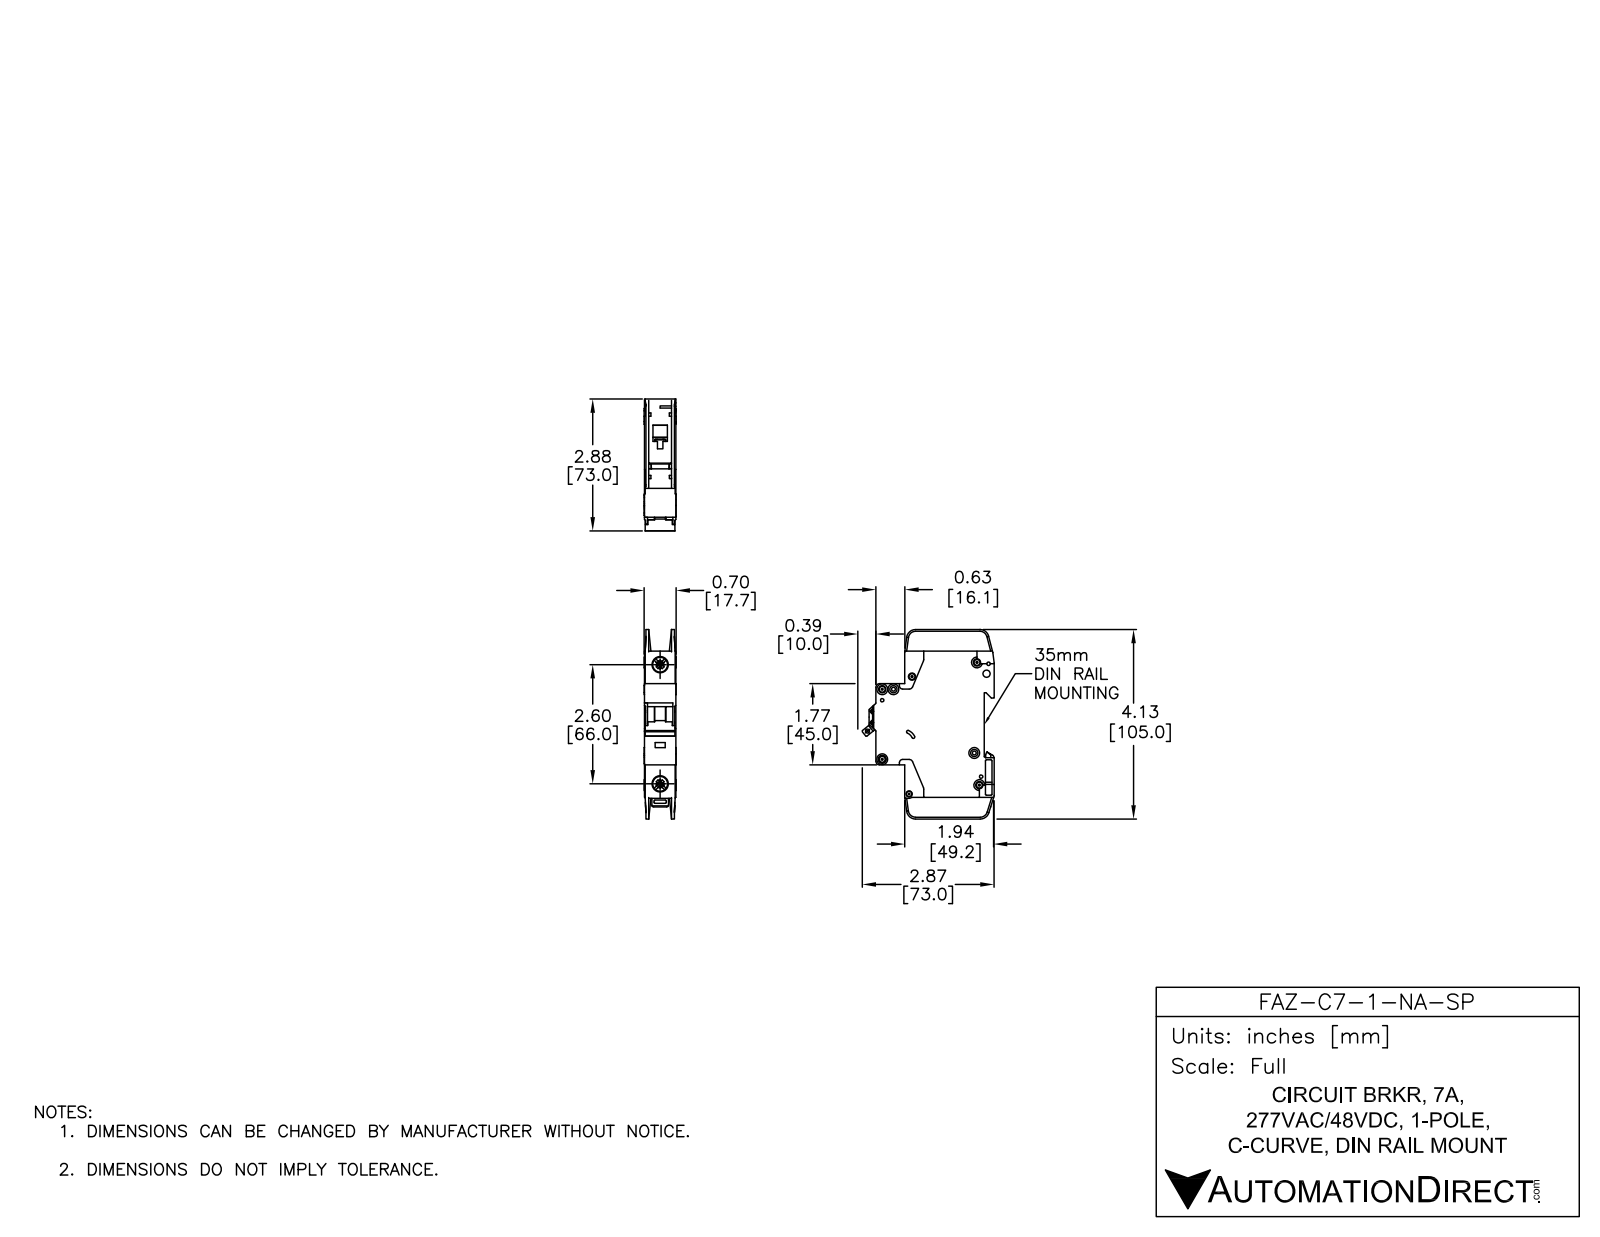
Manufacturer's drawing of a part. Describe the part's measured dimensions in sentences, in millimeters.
The part is named "FAZ-C7-1-NA-SP". Its 3-D file was written by "SolidWorks 2014 (AUTOMOTIVE_DESIGN)". It is 3 solids with 784 faces: 409 planar, 263 cylindrical and 112 other. Overall it measures 105 by 73.04 by 17.7 millimeters. Its volume is 77 695 cubic millimeters and its surface area 24 740 square millimeters. Round holes: 7 of diameter 3.6, 2 of diameter 1.09, 2 of diameter 1.5, 2 of diameter 4, 2 of diameter 7.15, 2 of diameter 8.2, 1 of diameter 1.9, 1 of diameter 2.15, 1 of diameter 2.2, 1 of diameter 2.55, 1 of diameter 3.3, 1 of diameter 3.4. Round bosses or shafts: 7 of diameter 6, 1 of diameter 2.5. Partial cylindrical surfaces (rounded edges, fillets, slot ends): 29 of radius 0.25, 18 of radius 0.5, 10 of radius 1, 10 of radius 2, 5 of radius 5, 4 of radius 4, 3 of radius 1.8, 2 of radius 0.2. The main face-to-face distances are 17.5, 15.05, 0.7, 2.45, 1.75, 15.75, 13.3, 14, 12.6, 2. The hole center spacings are 6.2, 5.19, 6.1, 8.19, 8.56, 8.7, 11.11, 12.45.
